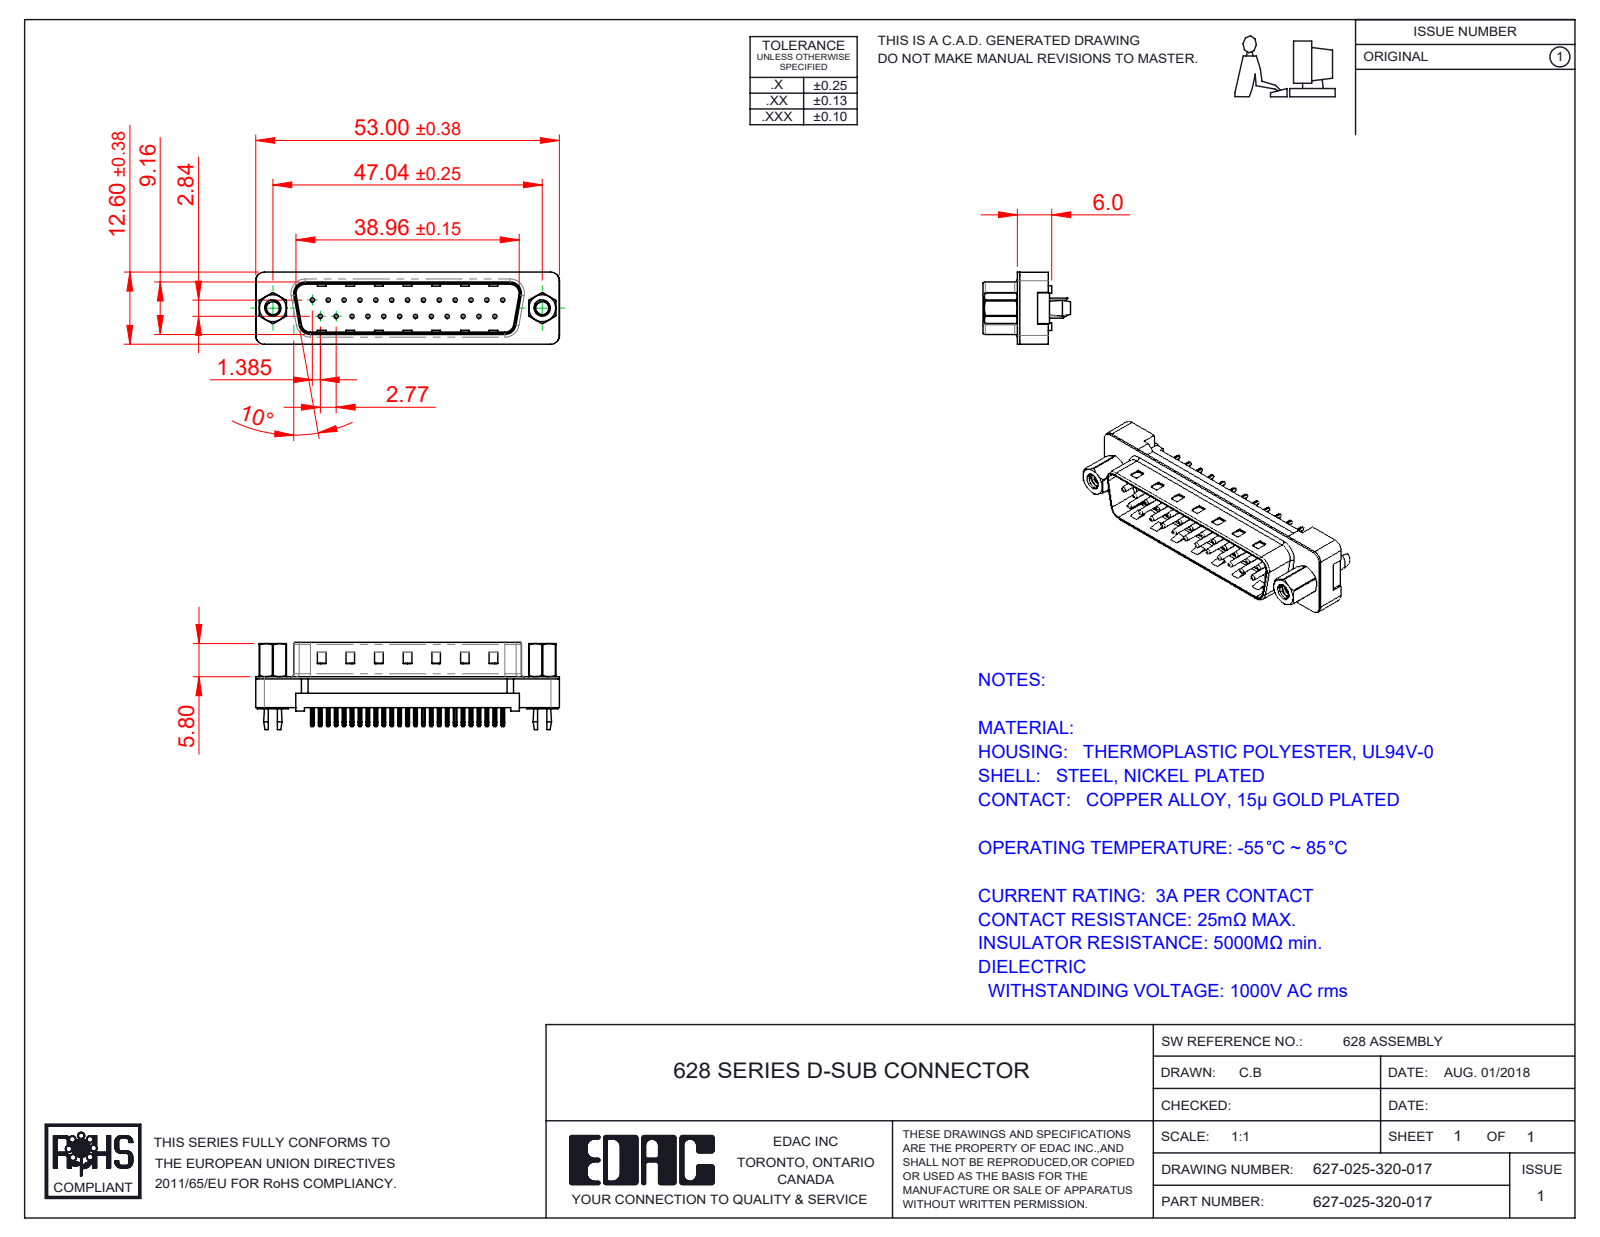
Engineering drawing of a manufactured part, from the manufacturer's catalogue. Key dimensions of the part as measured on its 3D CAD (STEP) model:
Part name (STEP PRODUCT): 627 PB Contact Row 1_20; 627 PB 4-40 Threaded Rivet with Boardlock; 627-025-320-017; 627 4-40 Hex Standoff (+3 more)
STEP written by: SolidWorks 2020 (CONFIG_CONTROL_DESIGN)
Units: millimetres
Bodies: 31 solids, 1909 faces (1185 planar, 570 cylindrical, 154 other)
Overall size (bounding box): 53.04 × 15.25 × 12.6
Volume: 2 785 mm³ · Surface area: 6 343 mm²
Round holes (diameter × count): ⌀0.35 ×25, ⌀0.85 ×25, ⌀2.26 ×2, ⌀2.29 ×2, ⌀4 ×2, ⌀4.8 ×2, ⌀5 ×2
Round bosses / shafts (diameter × count): ⌀0.75 ×25, ⌀4.9 ×2, ⌀2.79 ×2
Partial cylindrical surfaces — rounded edges, fillets, slot ends (radius × count): R0.25 ×50, R0.12 ×25, R0.5 ×8, R1.5 ×8, R0.9 ×4, R1.6 ×4, R2 ×4, R0.4 ×2
Main face-to-face distances: 0.4, 2.5, 8.76, 2.9, 5.4, 1.58, 5, 1.3, 6.5, 0.68
Hole centre spacings: 3.16, 5.54, 2.77, 11.08, 8.31, 5.03, 13.85, 16.62
